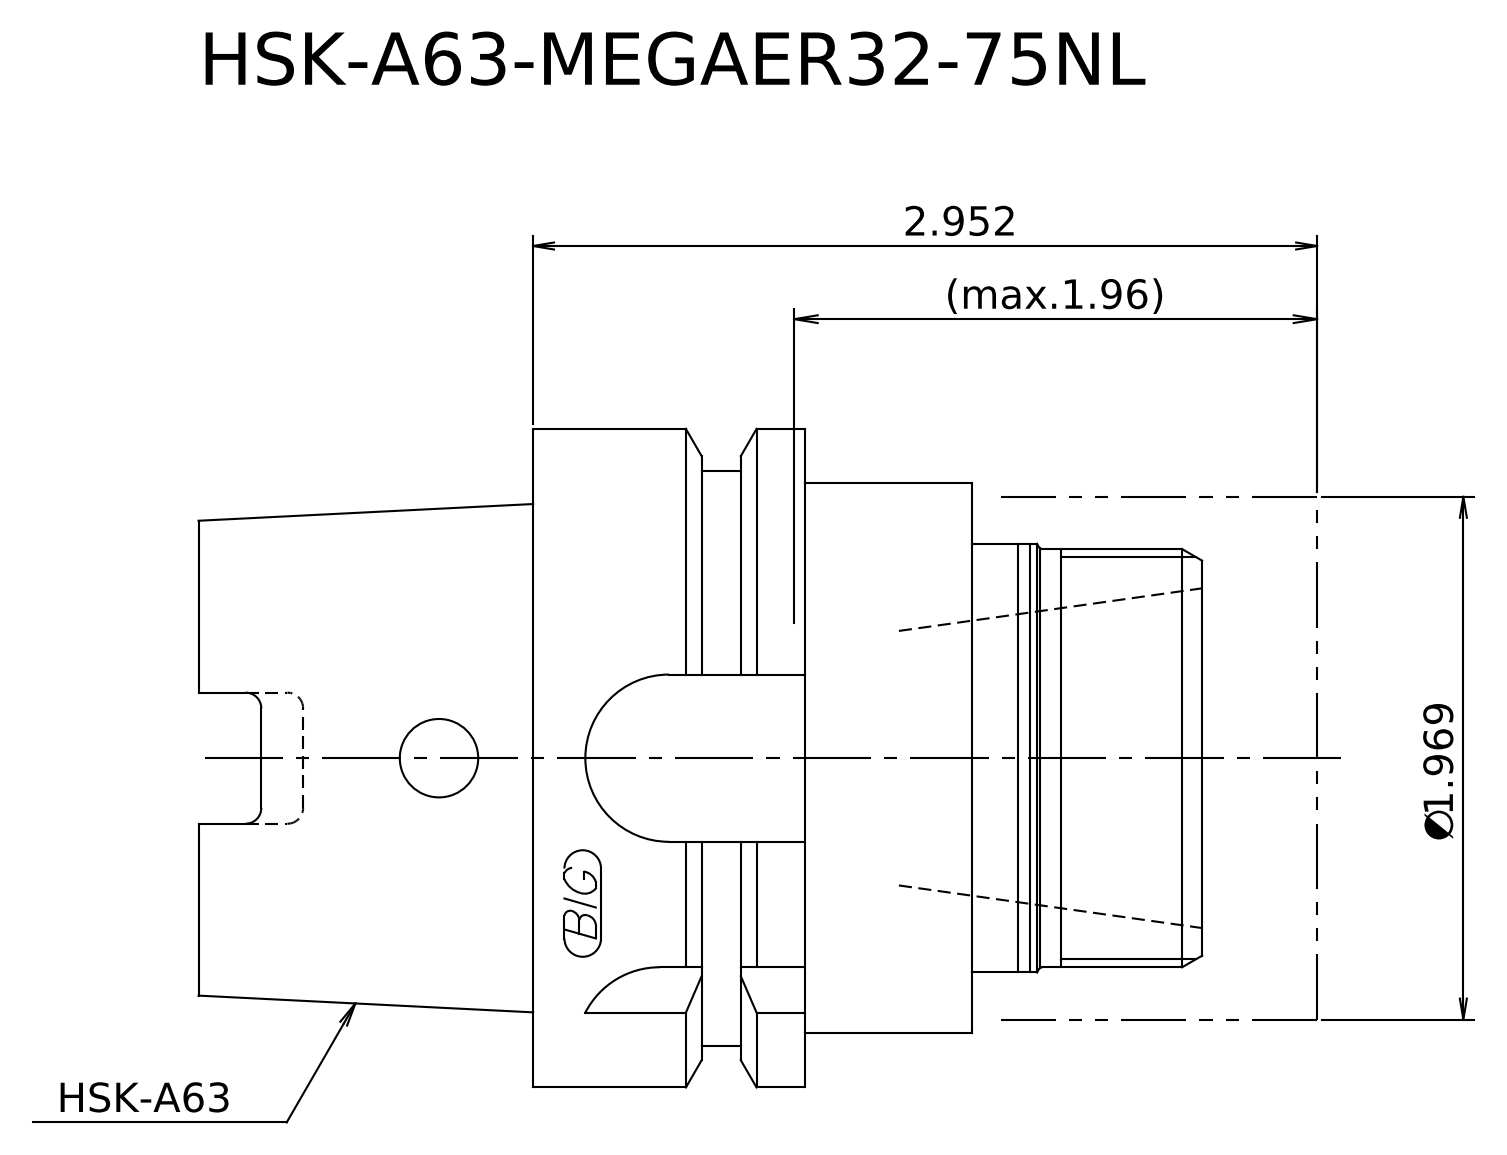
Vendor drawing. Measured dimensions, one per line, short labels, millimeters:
written by: Kubotek KeyCreator 2011 V10.0.2 (22737) (automotive_design)
unit: mm
bodies: 2 solids, 21 faces (9 planar, 7 cylindrical, 5 other)
size: 107 × 63 × 63
volume: 255 120 mm³; area: 30 781 mm²
bosses: 1× ⌀63, 1× ⌀55, 1× ⌀52.6, 1× ⌀50, 1× ⌀41, 1× ⌀40
face distances: 30.2, 107, 76.8, 75, 44.8, 32, 11, 19.2, 64, 96
